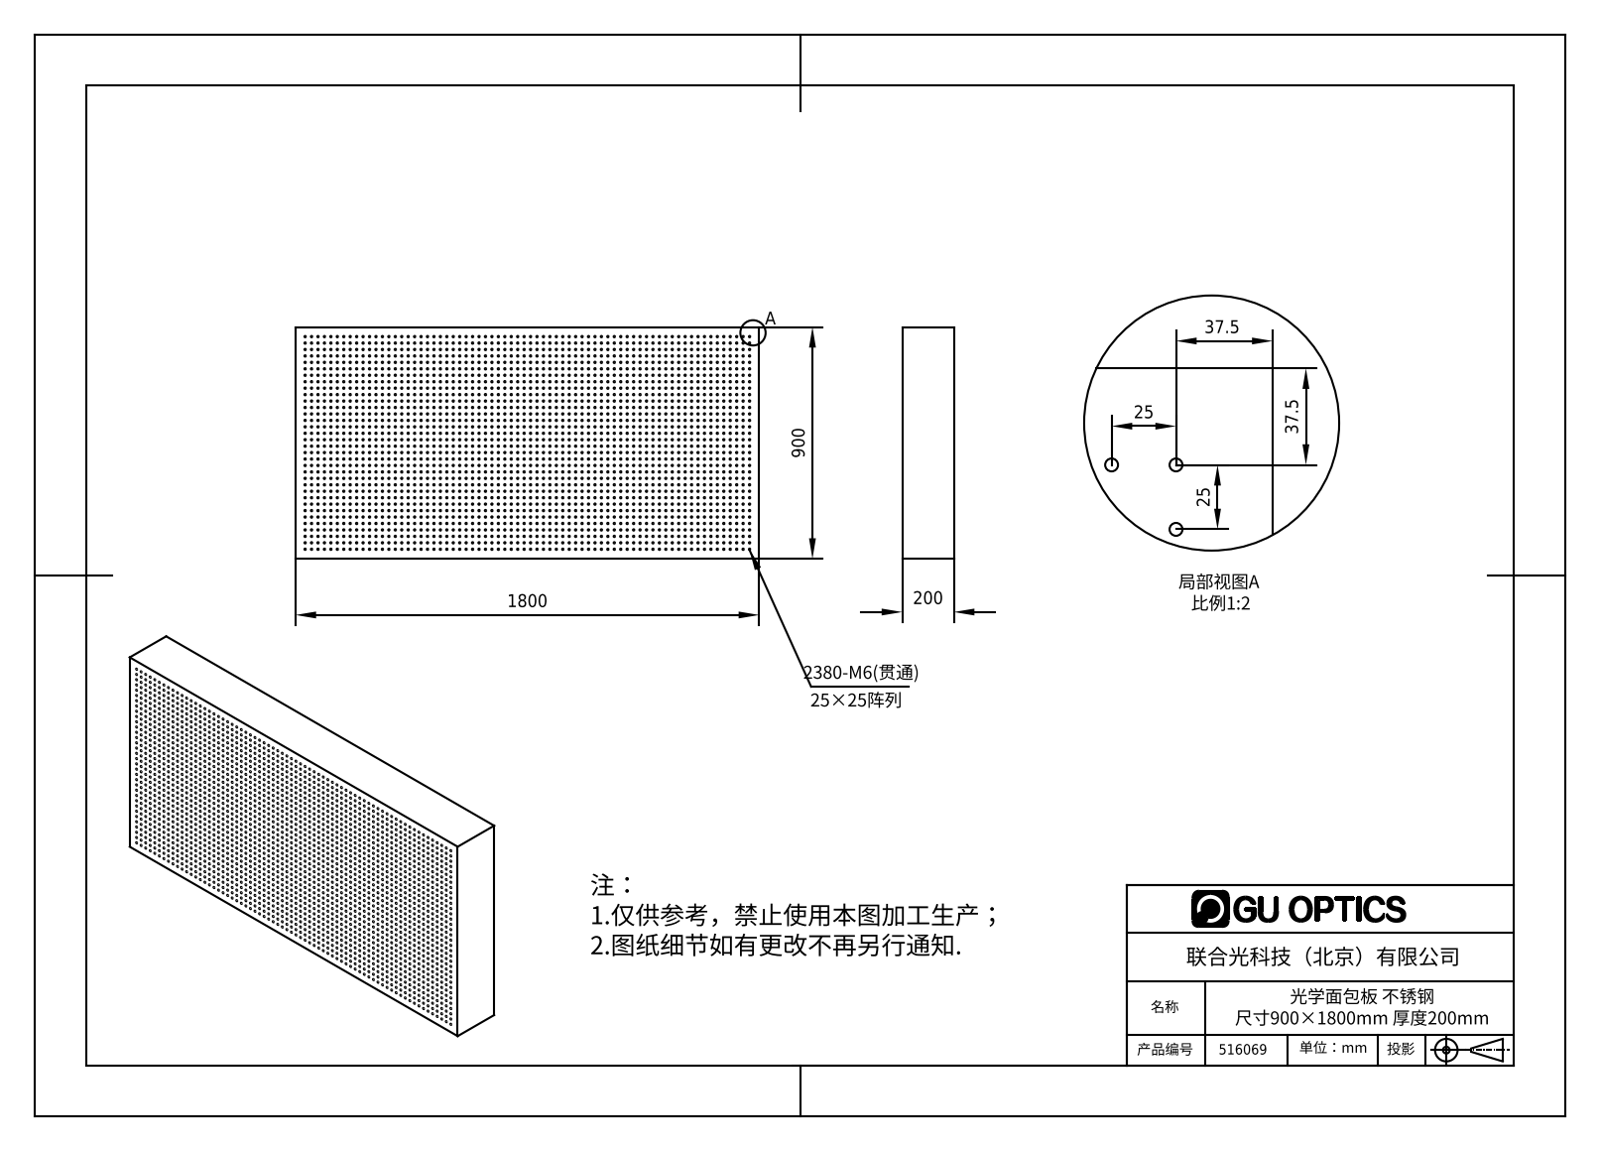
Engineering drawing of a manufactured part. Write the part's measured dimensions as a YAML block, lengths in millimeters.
part_name: "516069"
step_written_by: "SolidWorks 2016 (AUTOMOTIVE_DESIGN)"
units: millimeters
bodies: {solids: 1, faces: 4766, planar: 6, cylindrical: 4760, other: 0}
overall_size: [1800, 900, 200]
volume: 314700000
surface_area: 11700000
round_holes:
  - {diameter: 5, count: 2380}
face_to_face_distances: [200, 900, 1800]
hole_center_spacings: [25, 50, 75, 100, 125, 150, 175, 200]
